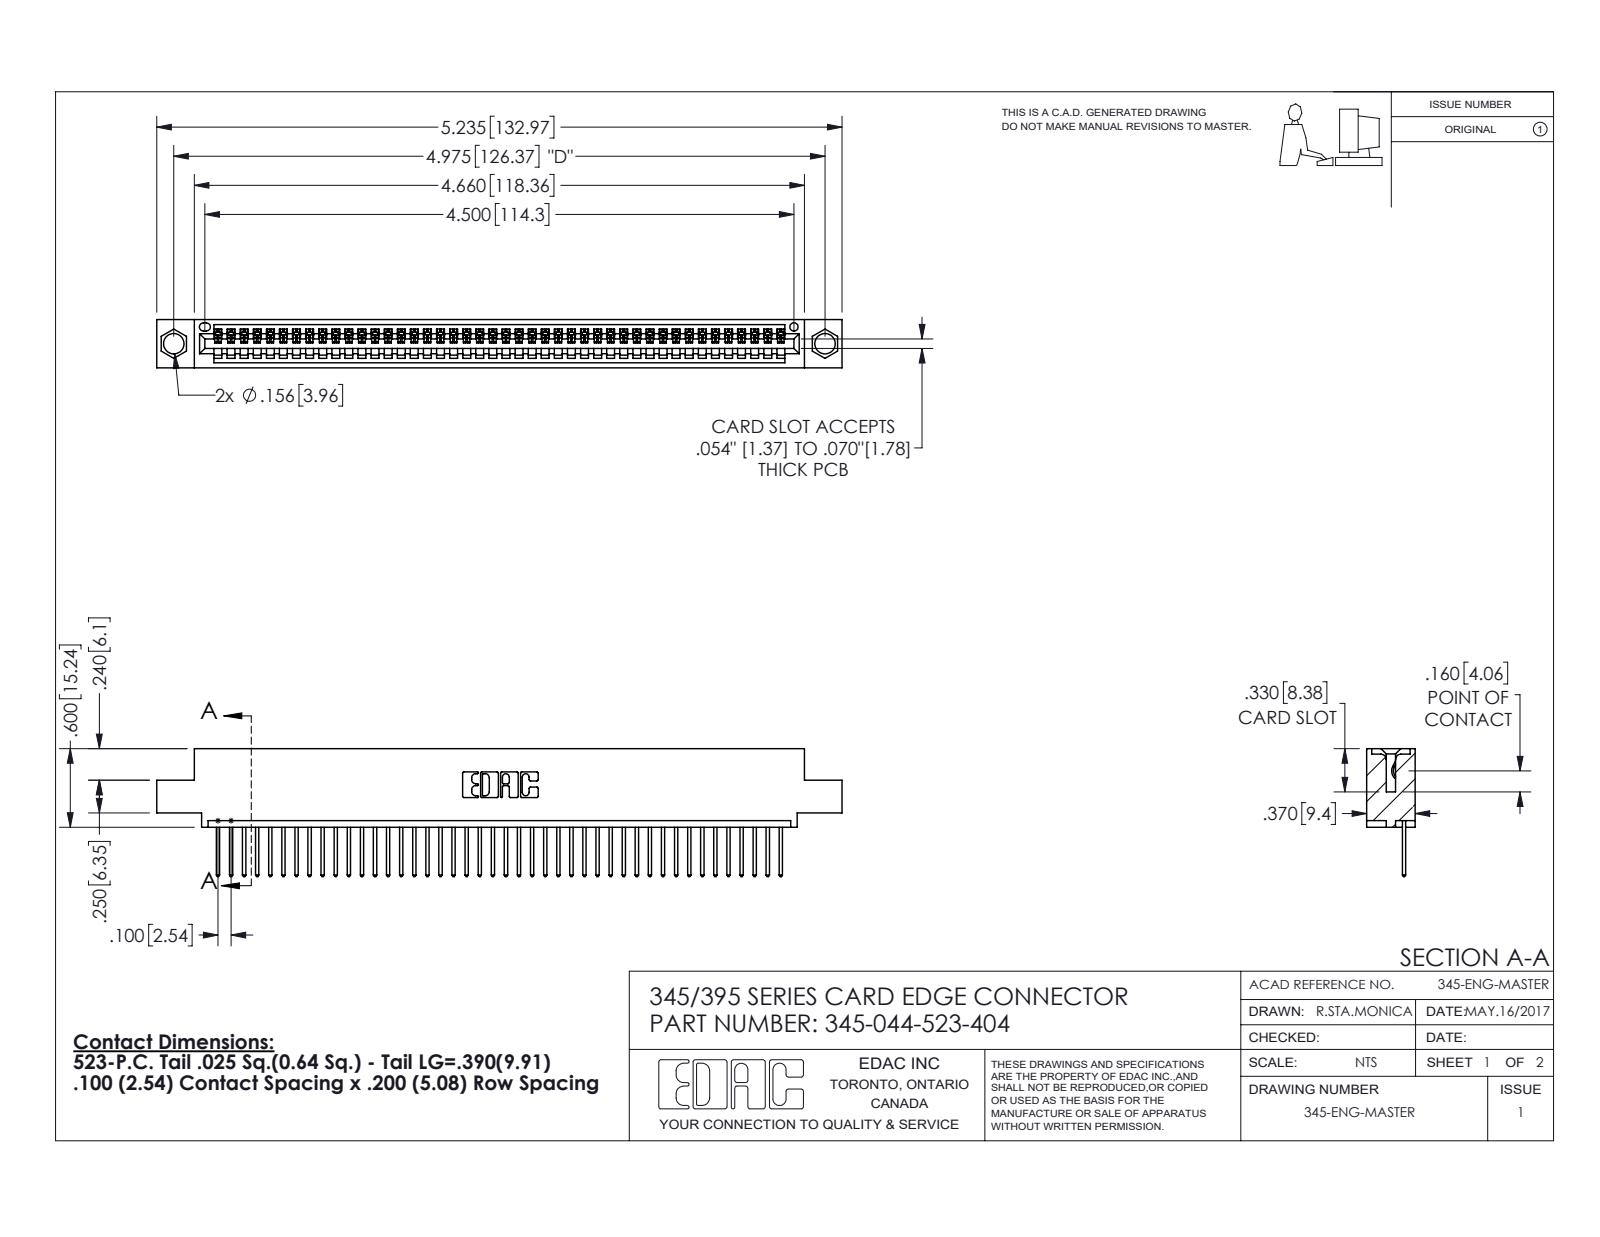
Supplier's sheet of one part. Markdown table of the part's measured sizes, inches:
| quantity | value |
| --- | --- |
| part name | 345-292-001_345-293-123; 345-044-523-404; 345 Part_0.110 Offset - 0.156 Dia-TH |
| STEP written by | SolidWorks 2016 (CONFIG_CONTROL_DESIGN) |
| units | inches |
| bodies | 45 solids, 2682 faces (1844 planar, 838 cylindrical, 0 other) |
| overall size | 5.235 × 0.977 × 0.37 |
| volume | 0.761 in³ |
| surface area | 25.63 in² |
| round holes (diameter × count) | 0.156 × 2, 0.064 × 1 |
| partial cylindrical surfaces (radius × count) | 0.006 × 88, 0.01 × 88, 0.01 × 22, 0.007 × 6, 0.031 × 6, 0.026 × 3, 0.031 × 2, 0.04 × 2 |
| main face-to-face distances | 0.072, 0.298, 0.37, 0.2, 0.098, 0.272, 0.025, 0.225, 0.149, 0.072 |
| hole center spacings | 0.27, 4.739, 4.975 |
